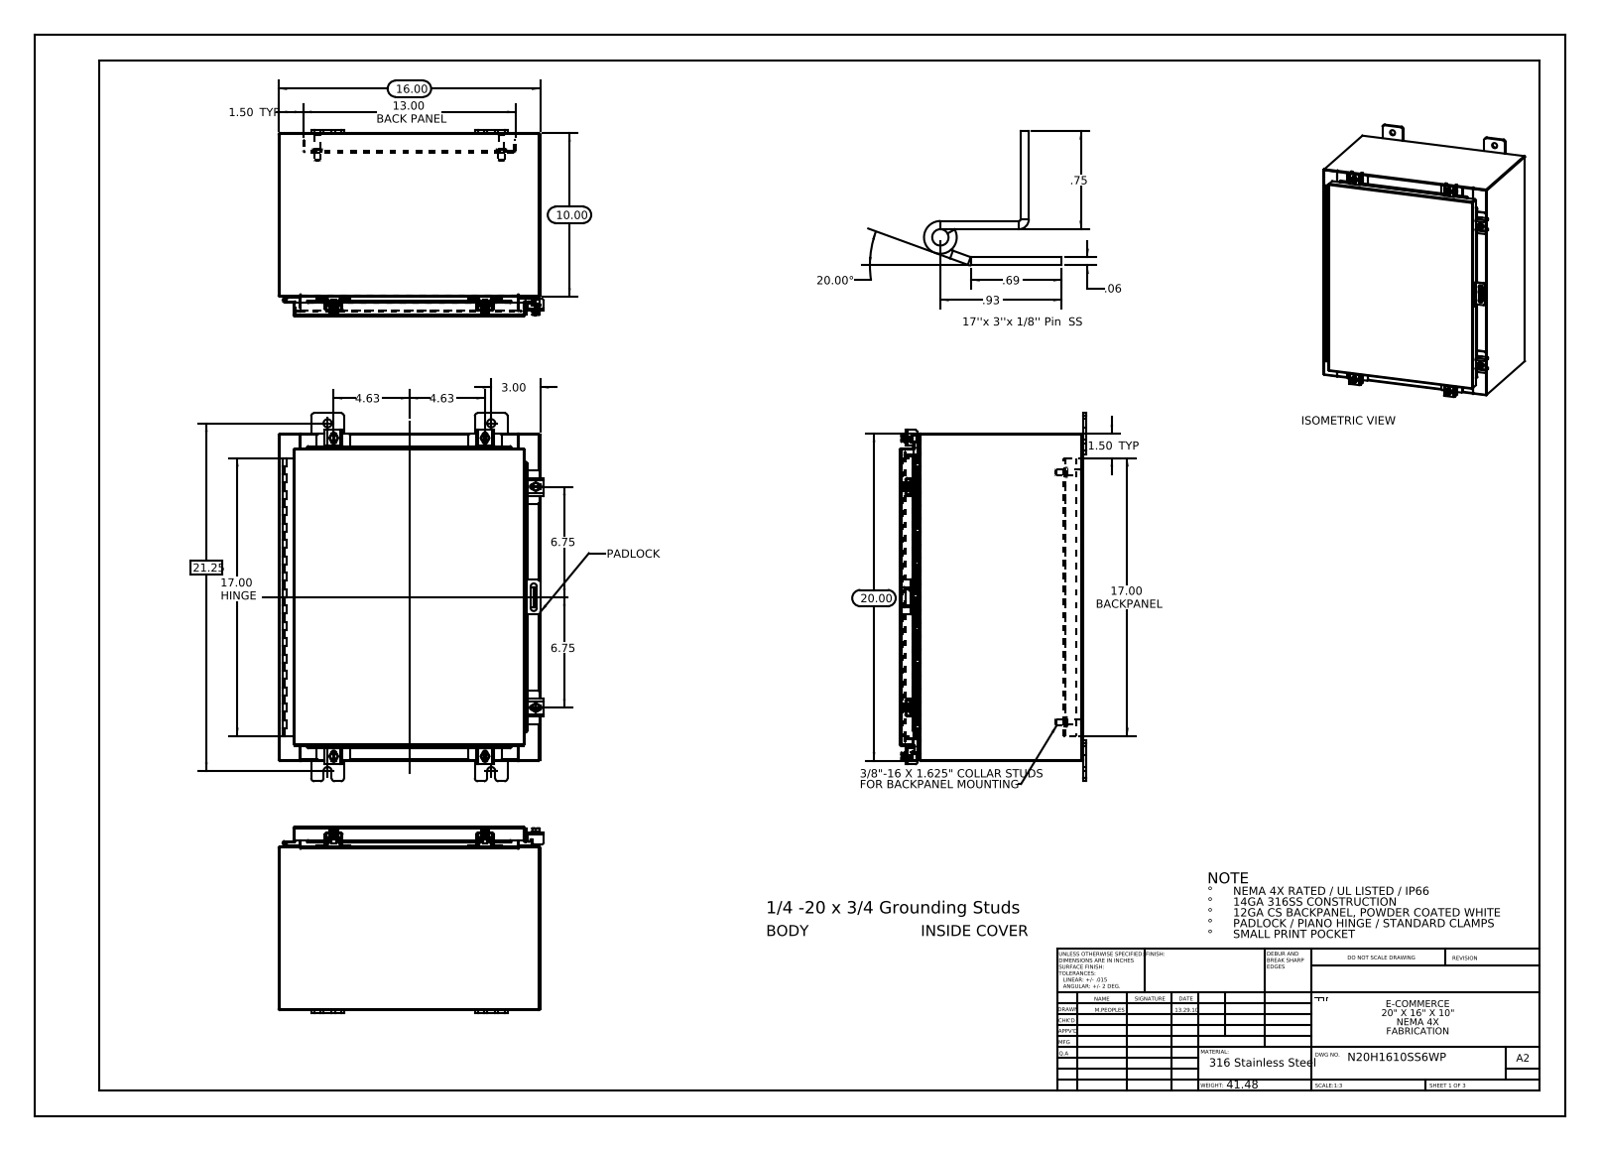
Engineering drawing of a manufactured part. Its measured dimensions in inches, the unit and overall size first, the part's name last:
Units: inches
Overall size (bounding box): 22.5 × 16.211 × 11.389
Round holes (diameter × count): ⌀0.5 ×8, ⌀0.213 ×6, ⌀0.26 ×6, ⌀0.125 ×2, ⌀0.125 ×1
Round bosses / shafts (diameter × count): ⌀0.25 ×7, ⌀0.5 ×6, ⌀0.399 ×6, ⌀0.625 ×4, ⌀0.375 ×4, ⌀0.33 ×4
Partial cylindrical surfaces — rounded edges, fillets, slot ends (radius × count): R0.06 ×30, R0.013 ×25, R0.19 ×24, R0.088 ×21, R0.12 ×12, R0.141 ×12, R0.125 ×10, R0.05 ×9
Main face-to-face distances: 0.075, 11.126, 15.925, 19.925, 11.201, 11.051, 0.104, 1, 1.075, 10.051
Hole centre spacings: 17.38, 1.858, 2.276, 2.326, 2.326, 3.065, 4.297, 9.25
Volume: 146.2 in³ · Surface area: 3 722 in²
Bodies: 47 solids, 1613 faces (860 planar, 657 cylindrical, 96 other)
Part name (STEP PRODUCT): N20H1610SS6WP Top; N20H1610SS6WP Padlock Hasp; N20H1610SS6WP Bottom; N20H1610SS6WP Mounting Feet (+8 more)
STEP written by: SolidWorks 2013 (CONFIG_CONTROL_DESIGN)
